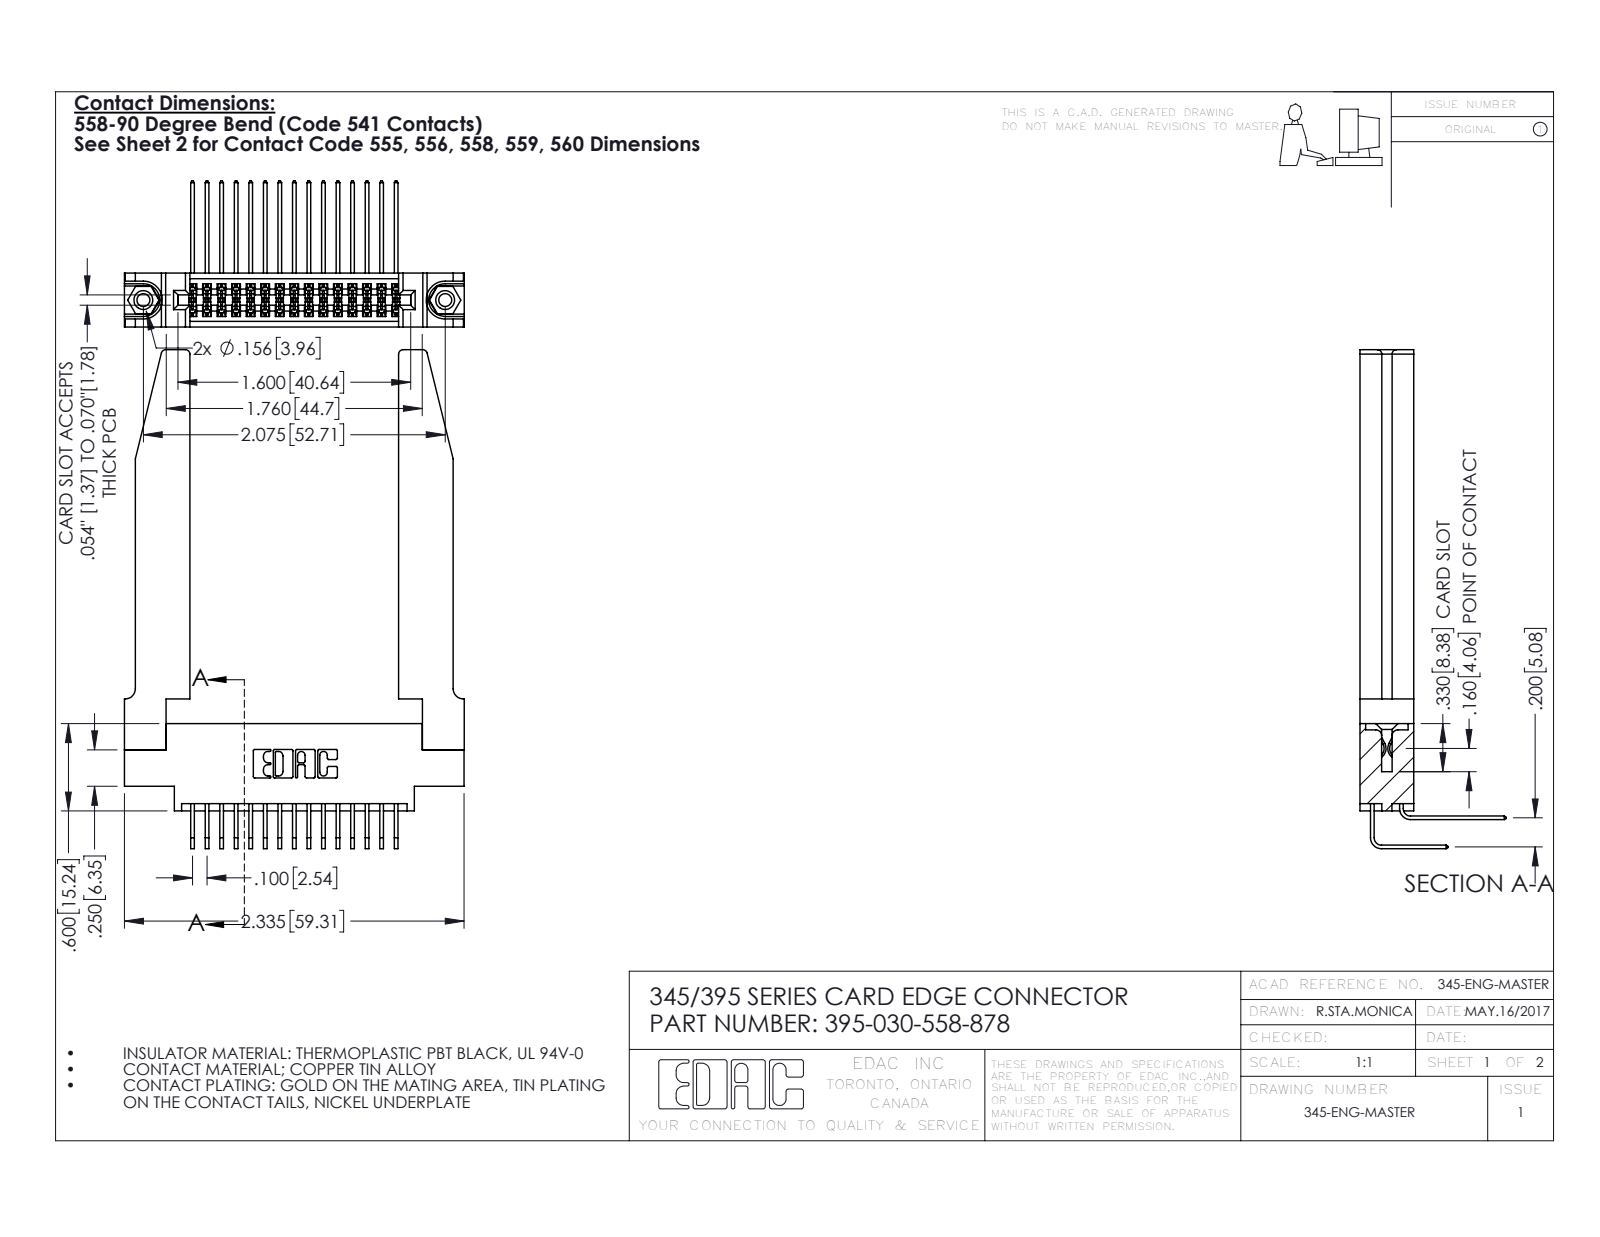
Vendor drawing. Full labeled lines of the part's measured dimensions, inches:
Part name (STEP PRODUCT): 345-220-078_345-220-078; 345 Part_0.170 Offset - 0.156 Dia-TH; 345-250-001_345-250-001-102; 345-292-001_558 559 Tail - 1 (+2 more)
STEP written by: SolidWorks 2016 (CONFIG_CONTROL_DESIGN)
Units: inches
Bodies: 35 solids, 1924 faces (1276 planar, 596 cylindrical, 52 other)
Overall size (bounding box): 3.429 × 2.336 × 1.005
Volume: 0.814 in³ · Surface area: 24.04 in²
Round holes (diameter × count): ⌀0.089 ×2, ⌀0.125 ×2, ⌀0.156 ×2, ⌀0.064 ×1
Round bosses / shafts (diameter × count): ⌀0.155 ×2
Partial cylindrical surfaces — rounded edges, fillets, slot ends (radius × count): R0.006 ×46, R0.01 ×22, R0.03 ×8, R0.007 ×6, R0.031 ×6, R0.026 ×3, R0.014 ×2, R0.019 ×2
Main face-to-face distances: 0.37, 0.072, 0.298, 0.2, 0.15, 0.148, 0.098, 0.272, 0.025, 0.22
Hole centre spacings: 0.27, 1.842, 2.075
